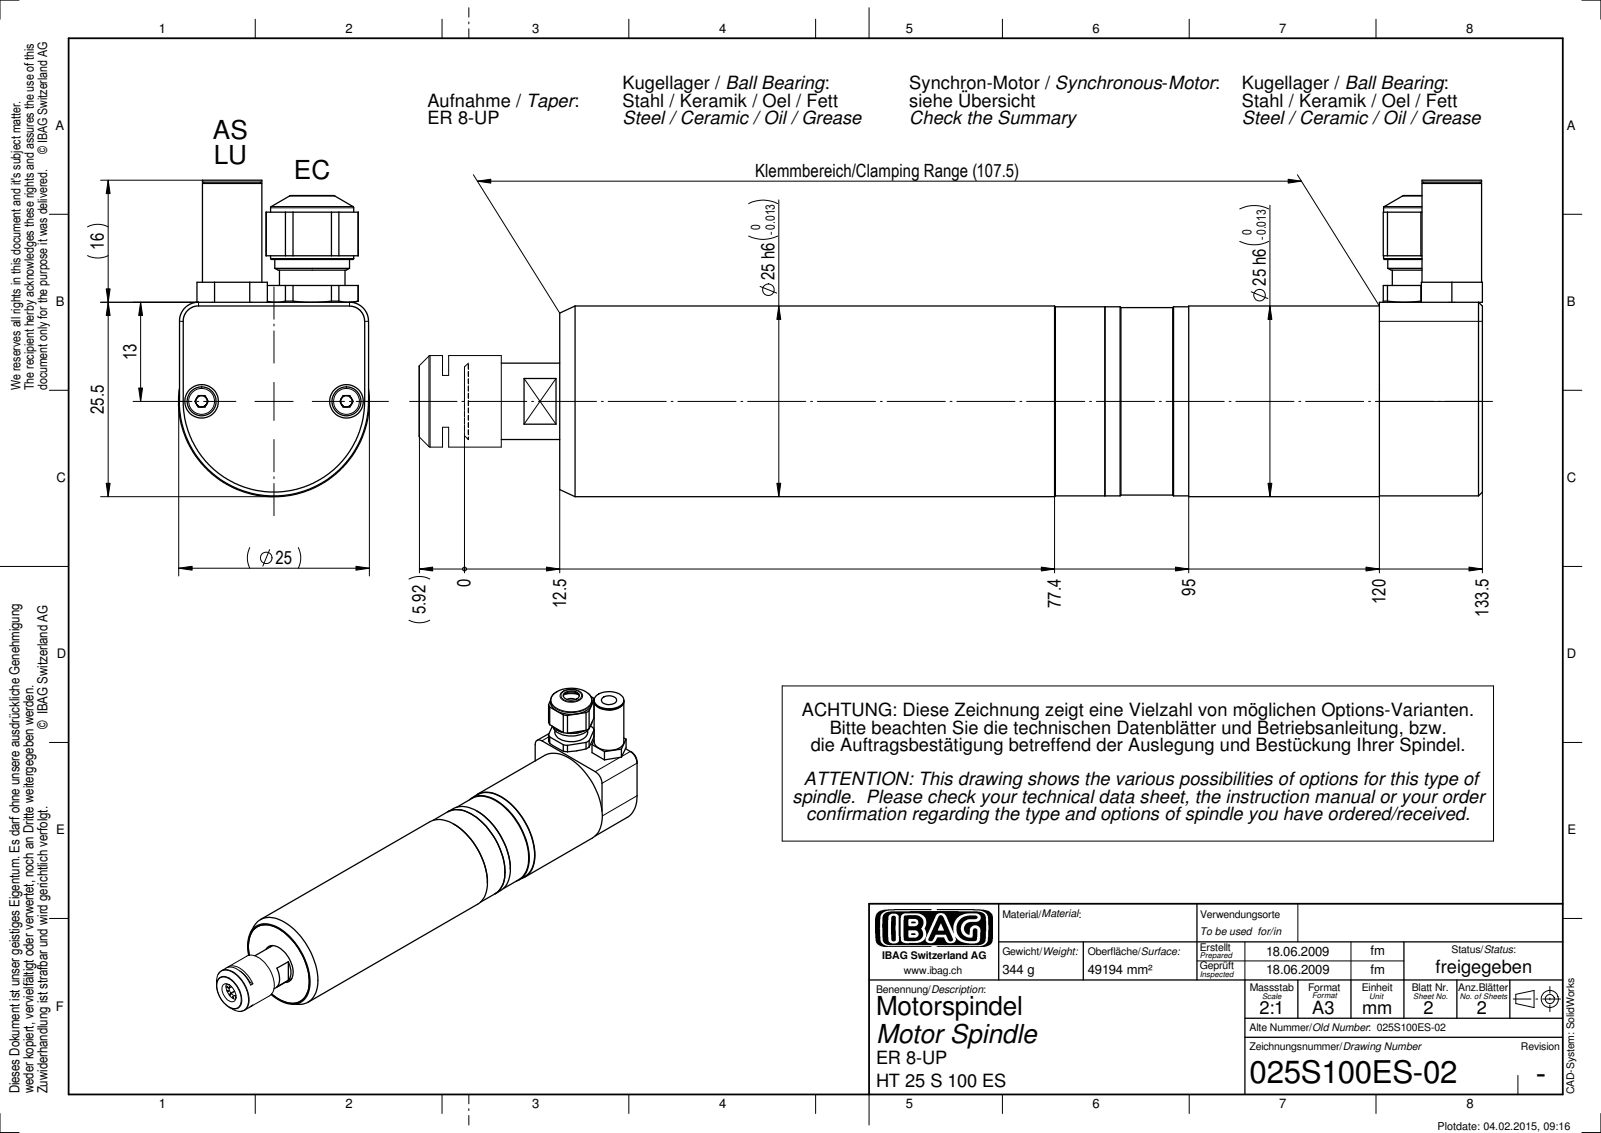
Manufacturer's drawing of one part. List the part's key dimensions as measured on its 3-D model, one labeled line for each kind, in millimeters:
Part name (STEP PRODUCT): 025S100ES-02
STEP written by: SolidWorks 2016 (CONFIG_CONTROL_DESIGN)
Units: millimetres
Bodies: 0 solids, 225 faces (109 planar, 75 cylindrical, 41 other)
Overall size (bounding box): 139.48 × 41.5 × 25
Round holes (diameter × count): ⌀3 ×2, ⌀4.4 ×2, ⌀4 ×1, ⌀4.2 ×1, ⌀5.2 ×1, ⌀9.15 ×1, ⌀10.6 ×1
Round bosses / shafts (diameter × count): ⌀3.8 ×2, ⌀25 ×1, ⌀24.8 ×1, ⌀24.6 ×1, ⌀12 ×1, ⌀10.9 ×1, ⌀10 ×1, ⌀9.79 ×1
Partial cylindrical surfaces — rounded edges, fillets, slot ends (radius × count): R2.5 ×2, R4.25 ×1, R6.05 ×1
Main face-to-face distances: 121, 1.8, 119.2, 71.5, 69.7, 49.5, 11, 107.5, 105.7, 36
Hole centre spacings: 9.5, 11.07, 19
